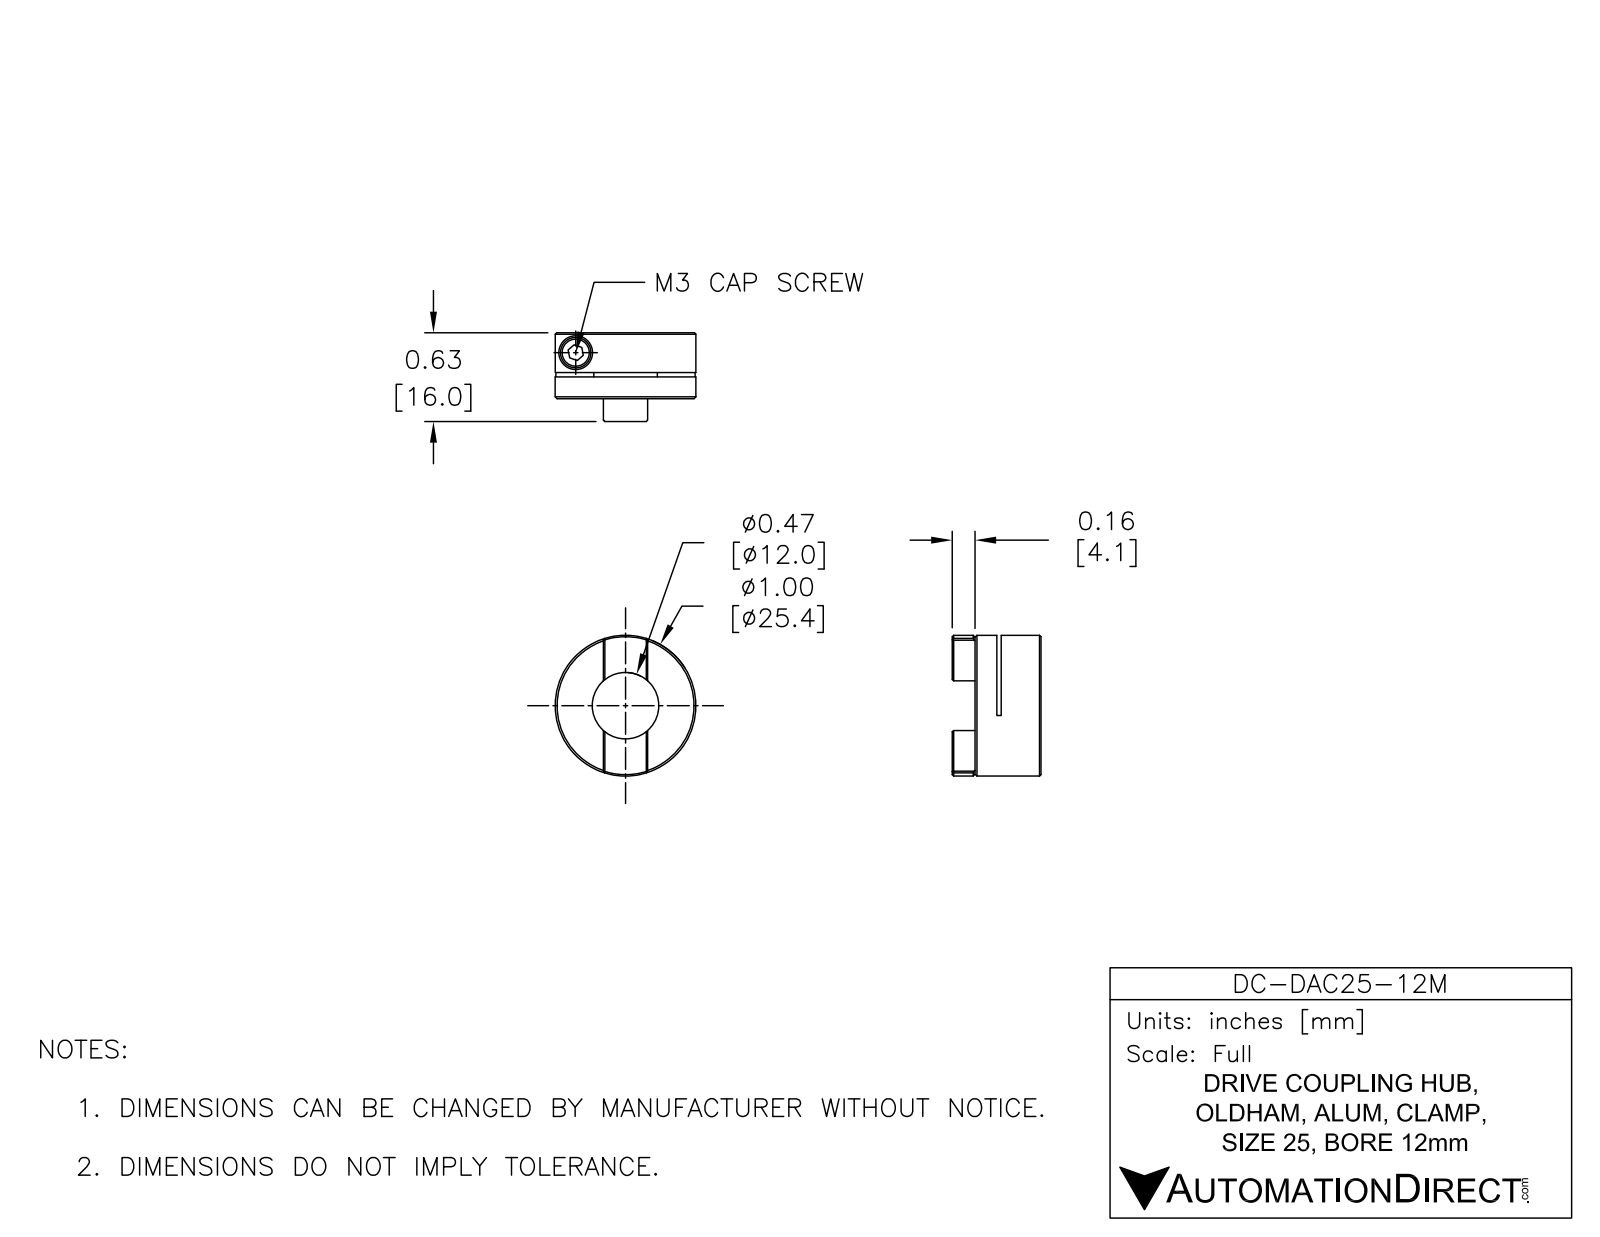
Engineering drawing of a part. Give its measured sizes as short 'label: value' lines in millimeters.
name: DC-DAC25-12M
written by: SolidWorks 2015 (AUTOMOTIVE_DESIGN)
unit: mm
bodies: 1 solid, 52 faces (27 planar, 15 cylindrical, 10 other)
size: 25.4 × 25.4 × 16
volume: 4 628 mm³; area: 3 054 mm²
holes: 1× ⌀2.46, 1× ⌀3.4, 1× ⌀6.1, 1× ⌀12
bosses: 1× ⌀25.4
rounds: 1× R25.4
face distances: 11.89, 7.95, 3.94, 7.16, 0.79, 4.73, 16, 8.84, 8.05, 4.11
